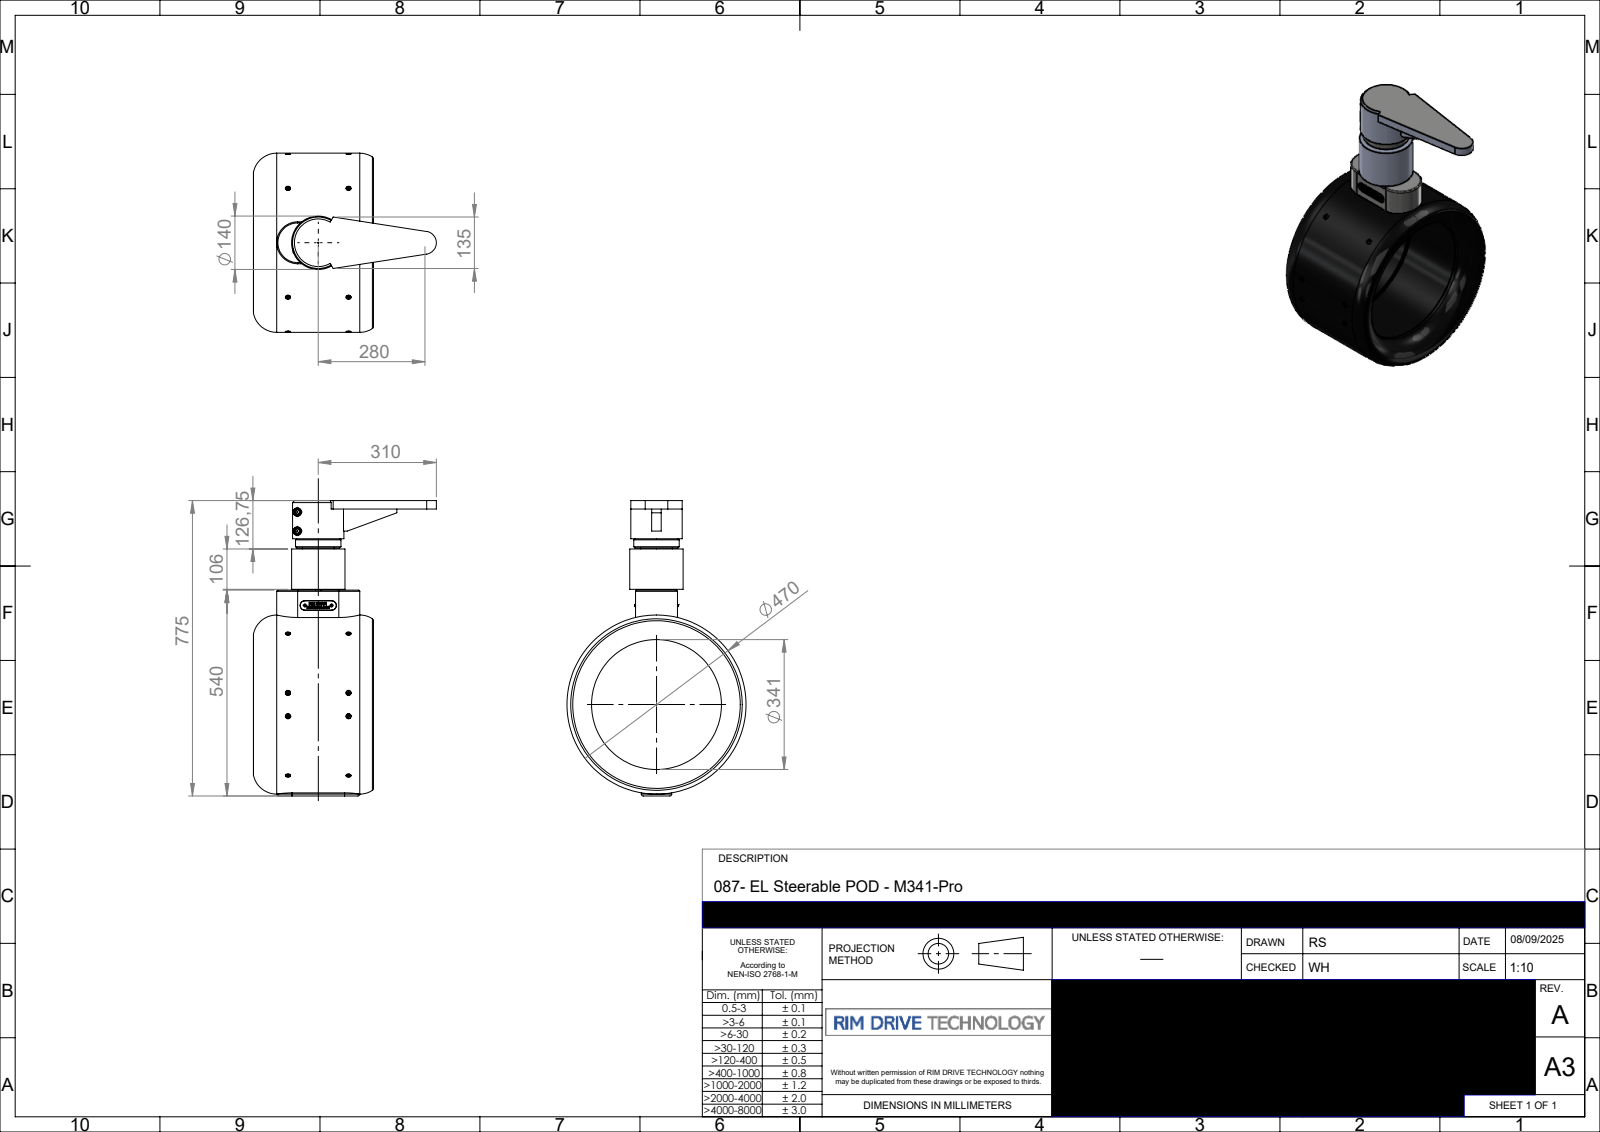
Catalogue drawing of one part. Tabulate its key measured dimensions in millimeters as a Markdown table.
| quantity | value |
| --- | --- |
| part name | P-087-330-rev-A-M341-Pro |
| STEP written by | SolidWorks 2024 (AUTOMOTIVE_DESIGN) |
| units | millimeters |
| bodies | 1 solid, 1067 faces (716 planar, 108 cylindrical, 243 other) |
| overall size | 775.1 × 480.13 × 470 |
| volume | 27 560 000 mm³ |
| surface area | 1 159 000 mm² |
| round holes (diameter × count) | 6.6 × 14, 4.2 × 2, 12 × 2, 22 × 2, 341 × 1, 360 × 1 |
| round bosses / shafts (diameter × count) | 11.57 × 22, 6 × 14, 21 × 2, 7.6 × 2, 4 × 2, 470 × 1, 140 × 1, 135 × 1 |
| partial cylindrical surfaces (radius × count) | 1 × 2, 3 × 2, 5 × 2, 12.4 × 2, 40 × 2, 55 × 2, 30 × 1, 230 × 1 |
| main face-to-face distances | 22, 753.1, 775.1, 540.1, 213, 235, 67.5, 42.5, 648.35, 108.25 |
| hole center spacings | 25, 160.95, 50, 159, 0.44, 166.68, 70, 196.12 |
